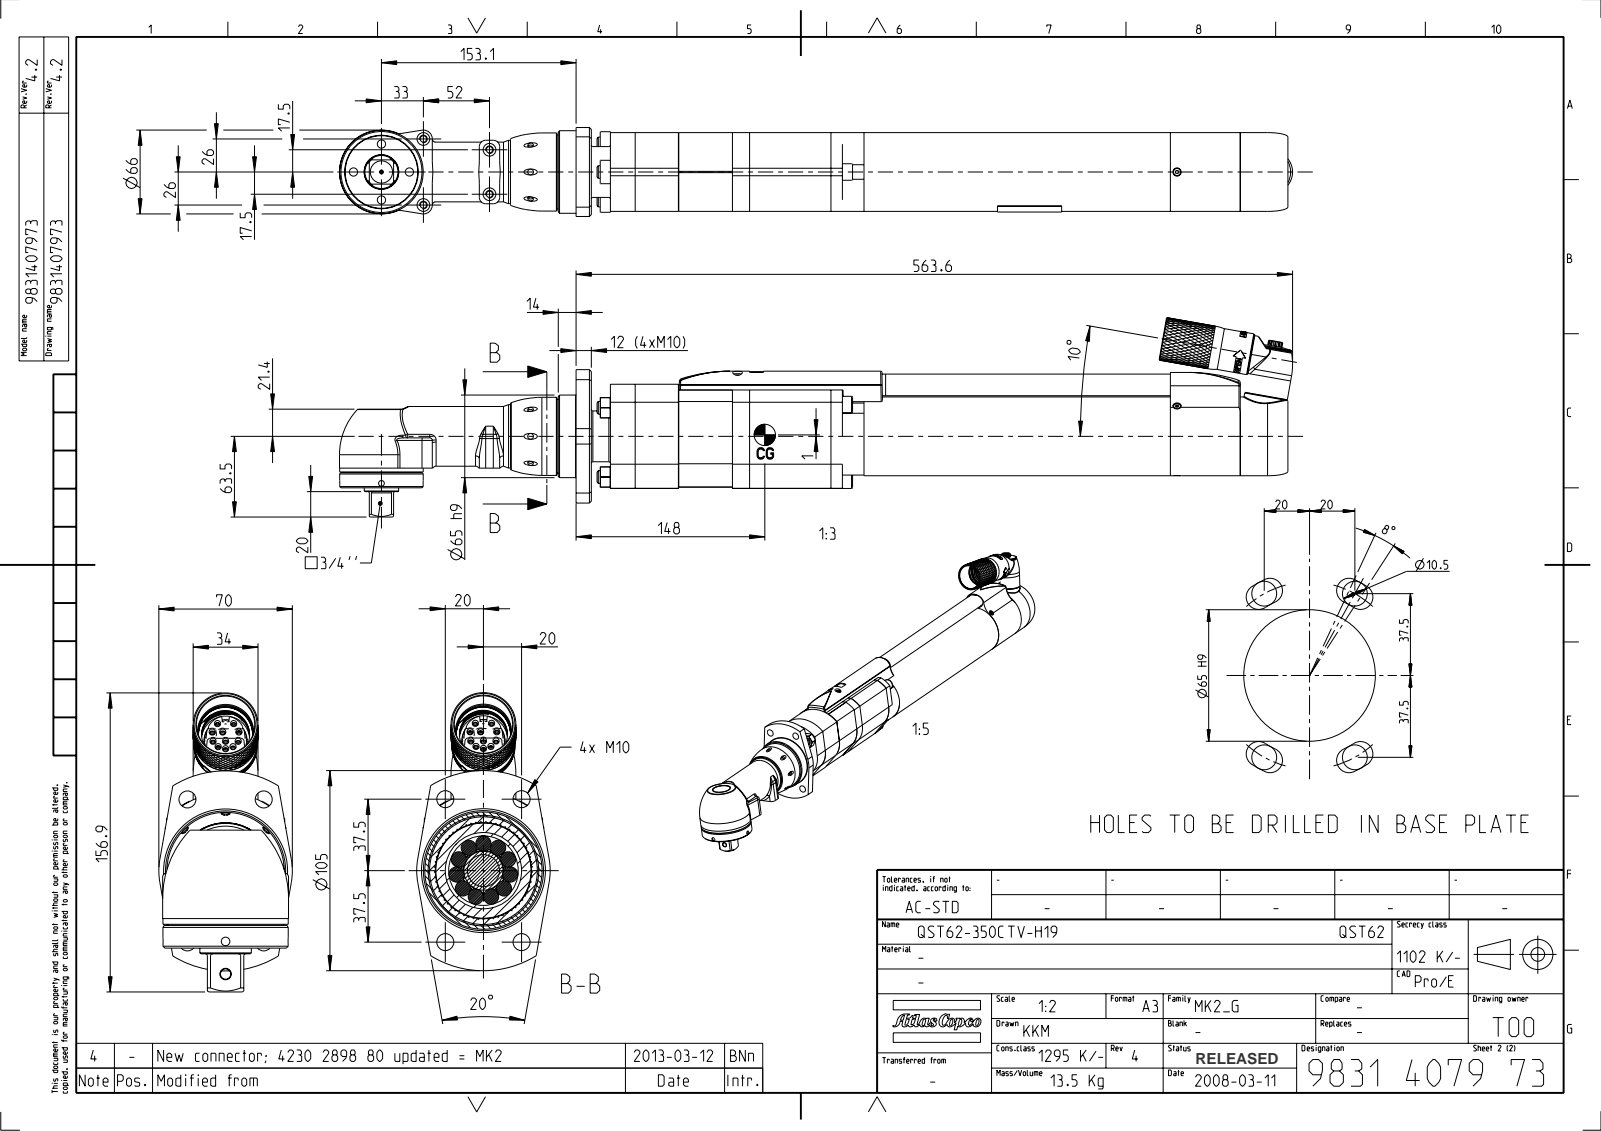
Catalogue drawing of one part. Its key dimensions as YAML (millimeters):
part_name: "4230260301; 4230260311_ASM; 4230265400; 0219110017 (+8 more)"
step_written_by: "PRO/ENGINEER BY PARAMETRIC TECHNOLOGY CORPORATION, 2012420 (CONFIG_CONTROL_DESIGN)"
units: millimeters
bodies: {solids: 37, faces: 5027, planar: 2065, cylindrical: 1613, other: 1349}
overall_size: [749.74, 156.9, 70]
volume: 1442000
surface_area: 528773
round_holes:
  - {diameter: 4.5, count: 14}
  - {diameter: 2.64, count: 11}
  - {diameter: 3.27, count: 11}
  - {diameter: 3.6, count: 11}
  - {diameter: 3.3, count: 7}
  - {diameter: 8.92, count: 7}
  - {diameter: 6.5, count: 5}
  - {diameter: 3.92, count: 4}
  - {diameter: 5, count: 4}
  - {diameter: 7.5, count: 4}
  - {diameter: 9, count: 4}
  - {diameter: 10, count: 4}
round_bosses_or_shafts:
  - {diameter: 10, count: 7}
  - {diameter: 8, count: 4}
  - {diameter: 5, count: 4}
  - {diameter: 34, count: 3}
  - {diameter: 13, count: 3}
  - {diameter: 3, count: 3}
  - {diameter: 2.5, count: 3}
  - {diameter: 62, count: 2}
partial_cylinders:
  - {radius: 1, count: 81}
  - {radius: 0.2, count: 58}
  - {radius: 0.1, count: 53}
  - {radius: 0.5, count: 43}
  - {radius: 5, count: 10}
  - {radius: 2, count: 7}
  - {radius: 0.29, count: 6}
  - {radius: 0.51, count: 6}
face_to_face_distances: [214.5, 62, 34.5, 90, 3.5, 71.5, 36.5, 12, 10, 56]
hole_center_spacings: [7.16, 7.42, 7.41, 22.5, 7.35, 7.4, 20.22, 20.24]
